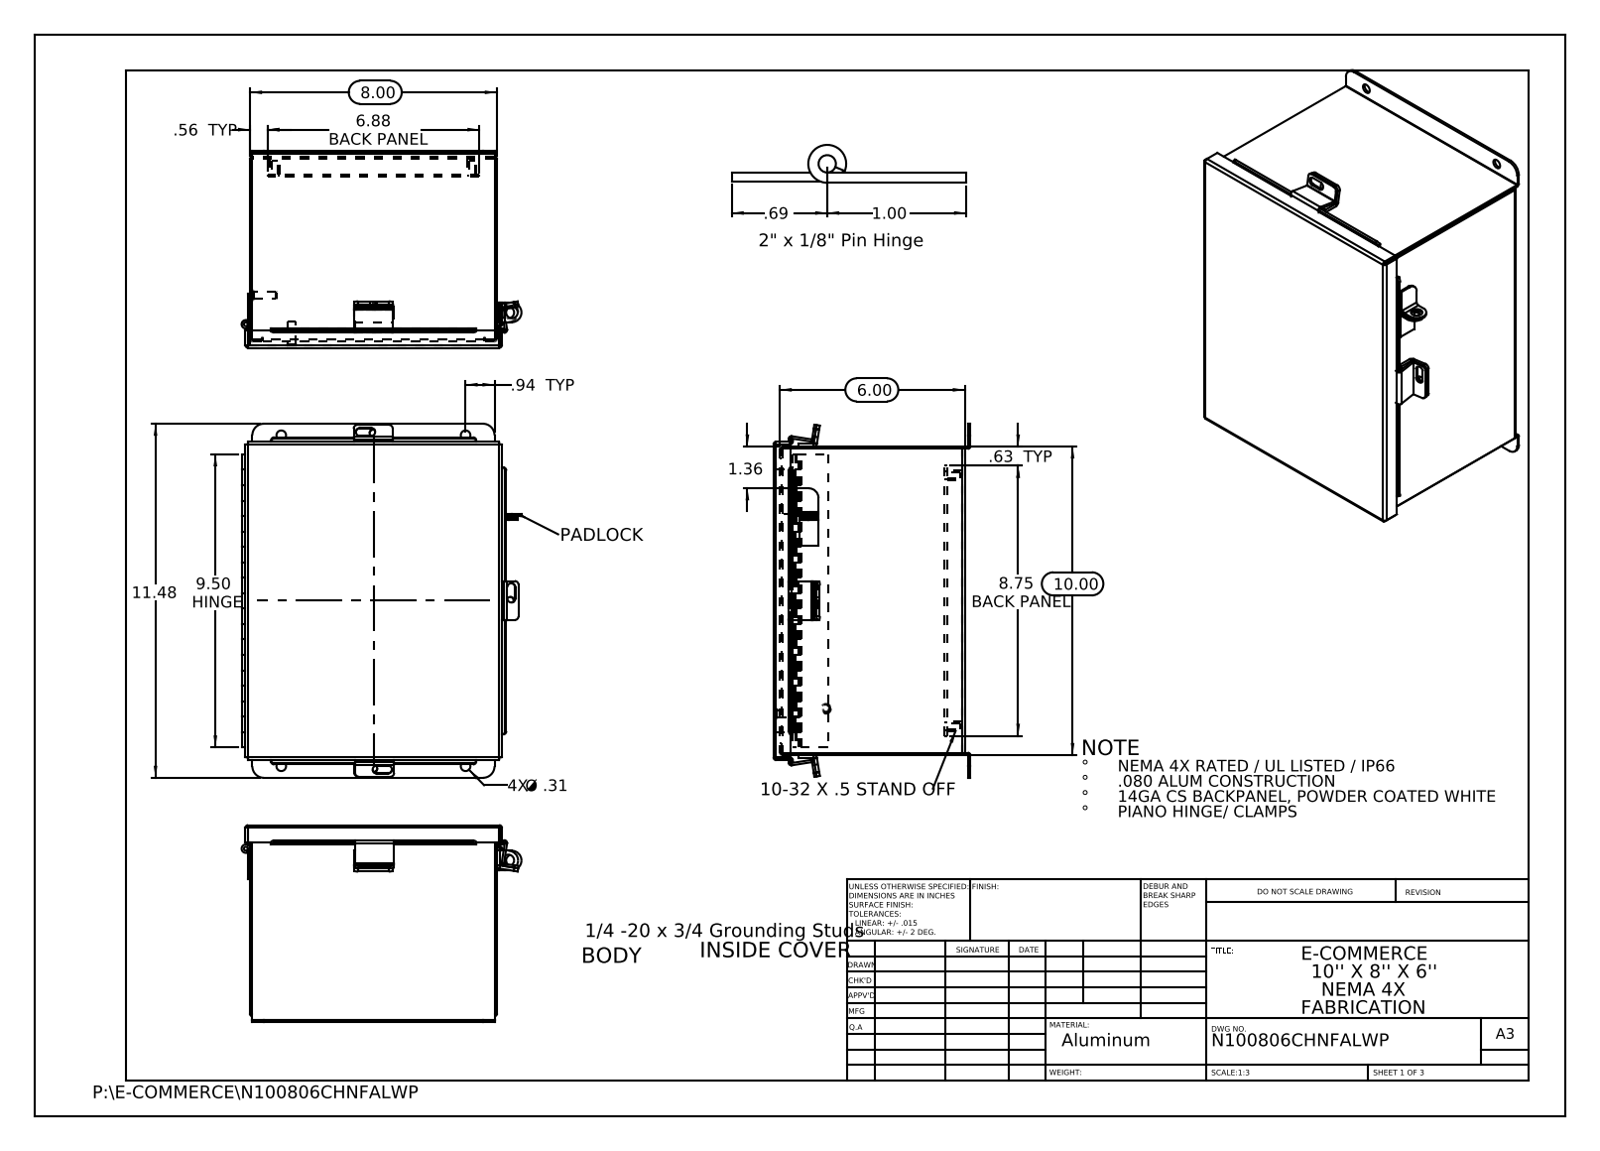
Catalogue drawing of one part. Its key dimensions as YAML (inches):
part_name: "N100806CHNFALWP HW-CD-S-25020-034; N100806CHNFALWP; N100806CHNFALWP JIC Backpanel; N100806CHNFALWP JIC_Cover_Template (+8 more)"
step_written_by: "SolidWorks 2013 (CONFIG_CONTROL_DESIGN)"
units: inches
bodies: {solids: 21, faces: 620, planar: 383, cylindrical: 217, other: 20}
overall_size: [11.476, 9.072, 6.39]
volume: 38.22
surface_area: 1047
round_holes:
  - {diameter: 0.25, count: 7}
  - {diameter: 0.187, count: 4}
  - {diameter: 0.312, count: 4}
  - {diameter: 0.125, count: 1}
  - {diameter: 0.373, count: 1}
  - {diameter: 0.375, count: 1}
round_bosses_or_shafts:
  - {diameter: 0.313, count: 4}
  - {diameter: 0.315, count: 2}
  - {diameter: 0.236, count: 2}
  - {diameter: 0.273, count: 1}
  - {diameter: 0.25, count: 1}
partial_cylinders:
  - {radius: 0.013, count: 13}
  - {radius: 0.009, count: 12}
  - {radius: 0.088, count: 12}
  - {radius: 0.125, count: 10}
  - {radius: 0.083, count: 6}
  - {radius: 0.1, count: 6}
  - {radius: 0.133, count: 6}
  - {radius: 0.375, count: 4}
face_to_face_distances: [0.075, 6.128, 7.925, 9.925, 6.053, 6.203, 0.074, 0.575, 0.5, 5.553]
hole_center_spacings: [1.315, 6.311, 9.428, 11.269, 5.976, 6.375, 8.126, 10.328]
